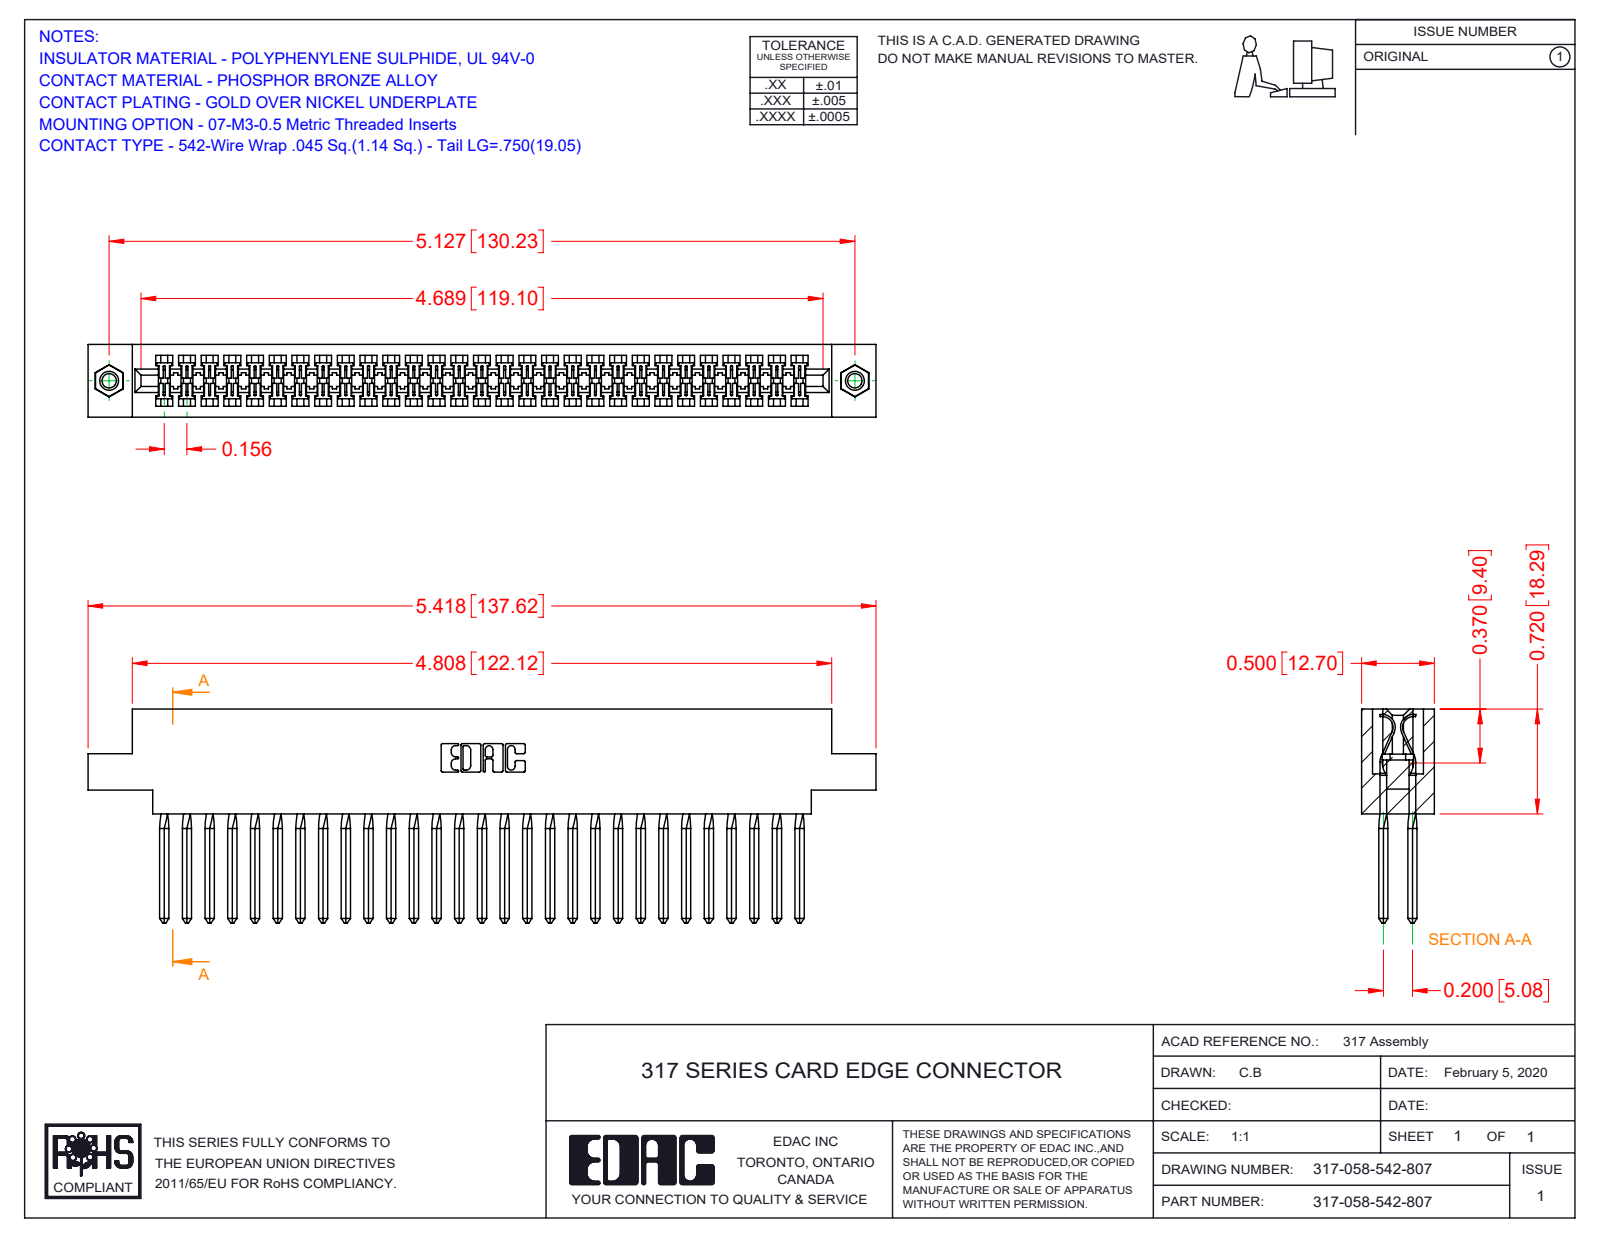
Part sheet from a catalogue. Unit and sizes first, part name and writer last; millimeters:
Units: millimetres
Overall size (bounding box): 137.6 × 37.3 × 12.7
Round holes (diameter × count): ⌀2.5 ×2, ⌀3.2 ×2, ⌀4 ×2
Round bosses / shafts (diameter × count): ⌀3.9 ×2
Partial cylindrical surfaces — rounded edges, fillets, slot ends (radius × count): R0.2 ×116, R0.3 ×22, R0.2 ×6, R0.8 ×6, R0.7 ×3, R1.9 ×2, R2.3 ×2, R2.5 ×2
Main face-to-face distances: 12.7, 1.9, 10.8, 8.9, 5.1, 2.8, 1.2, 2.9, 3.5, 3.3
Hole centre spacings: 130.2
Volume: 22 110 mm³ · Surface area: 30 370 mm²
Bodies: 61 solids, 3468 faces (2758 planar, 462 cylindrical, 248 other)
Part name (STEP PRODUCT): 317 Part_.156 Dia - TI; 345-250-001_345-250-005-103; 317-290-003_542; 317-058-542-807
STEP written by: SolidWorks 2016 (CONFIG_CONTROL_DESIGN)
